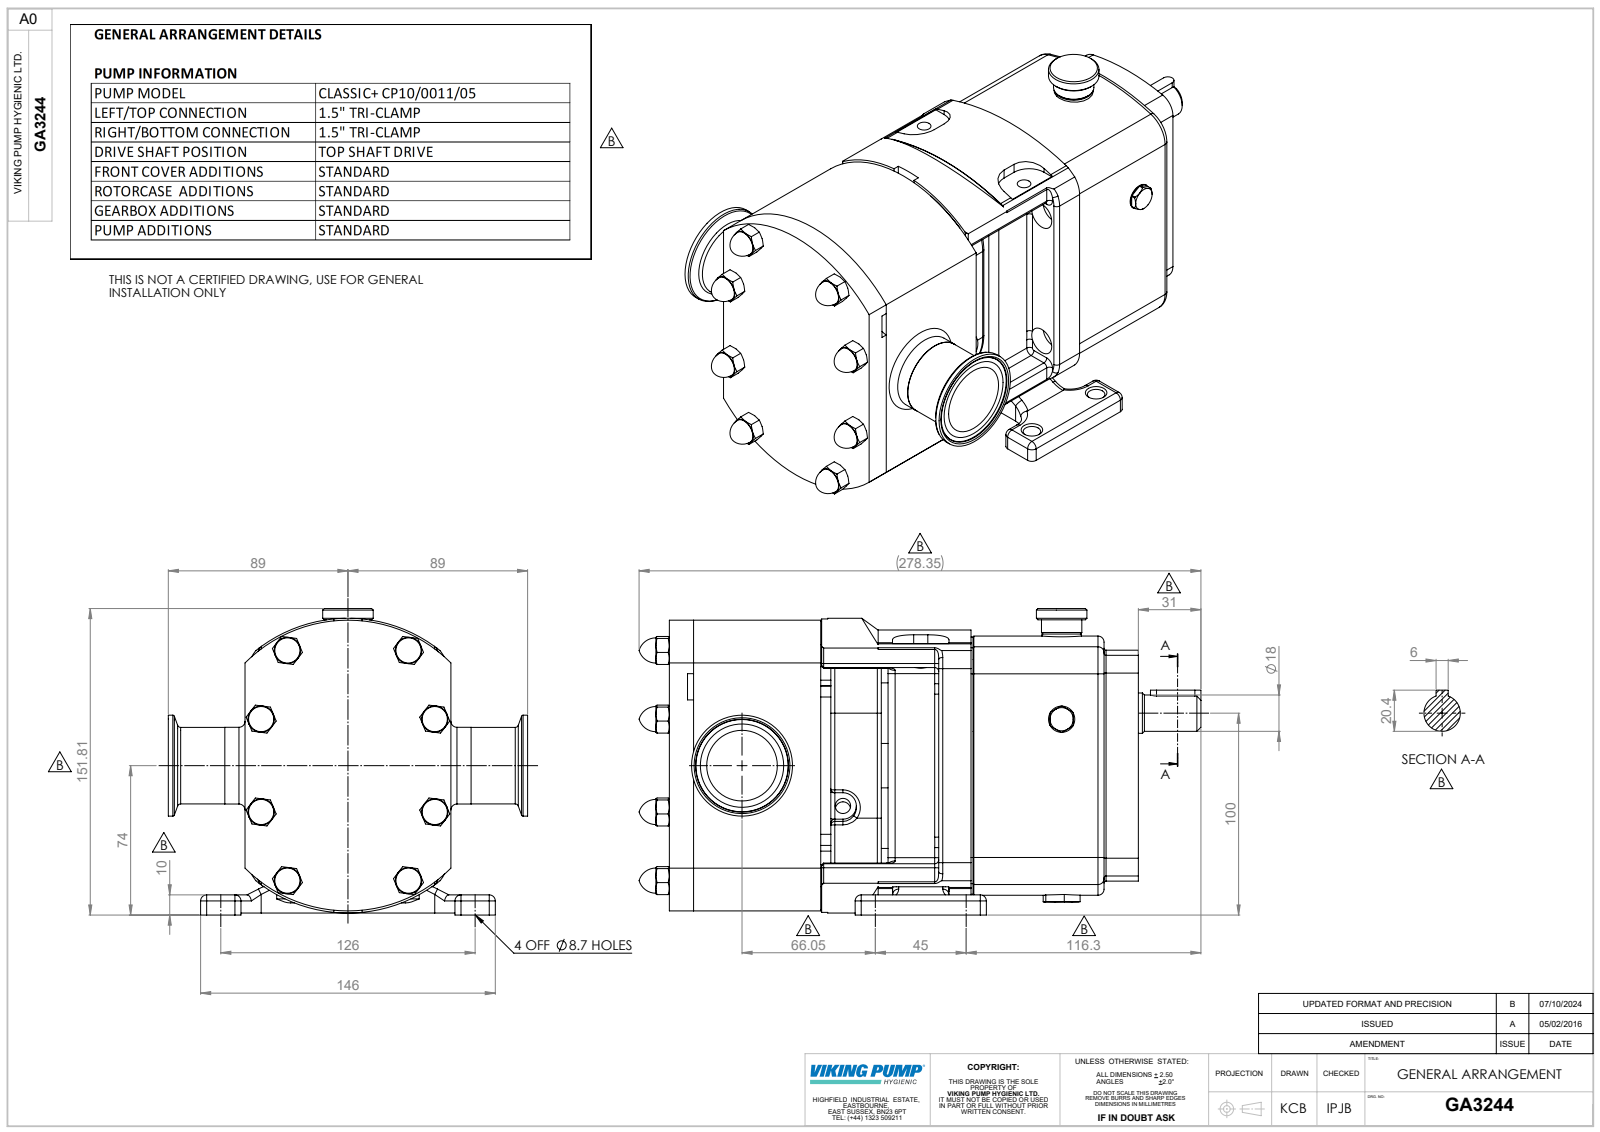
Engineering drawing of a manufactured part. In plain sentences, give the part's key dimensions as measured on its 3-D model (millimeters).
The part is named "Copy of Z94-5121-22 - 1.5 INCH^GA3244; Copy (2) of CP10-0011-05 H T^GA3244; GA3244". Its 3-D file was written by "SolidWorks 2023 (AUTOMOTIVE_DESIGN)". It is 3 solids with 762 faces: 252 planar, 218 cylindrical and 292 other. Overall it measures 278.35 by 178 by 151.81 millimeters. Its volume is 2 611 000 cubic millimeters and its surface area 196 796 square millimeters. Round holes: 4 of diameter 8.7, 4 of diameter 14, 2 of diameter 6.8, 2 of diameter 7.63, 1 of diameter 22.53, 1 of diameter 35. Round bosses or shafts: 2 of diameter 30, 1 of diameter 50, 1 of diameter 38, 1 of diameter 37.9, 1 of diameter 25.02, 1 of diameter 19.99, 1 of diameter 19.98, 1 of diameter 19.5. Partial cylindrical surfaces (rounded edges, fillets, slot ends): 30 of radius 2, 26 of radius 3, 12 of radius 13.5, 8 of radius 10.5, 6 of radius 3.5, 4 of radius 5.5, 4 of radius 6, 4 of radius 9. The main face-to-face distances are 5, 102, 232.35, 124, 96.99, 5.01, 91.99, 97, 108.35, 105. The hole center spacings are 35.92, 100.55, 45, 76, 77.02, 108.2, 126, 133.79.
